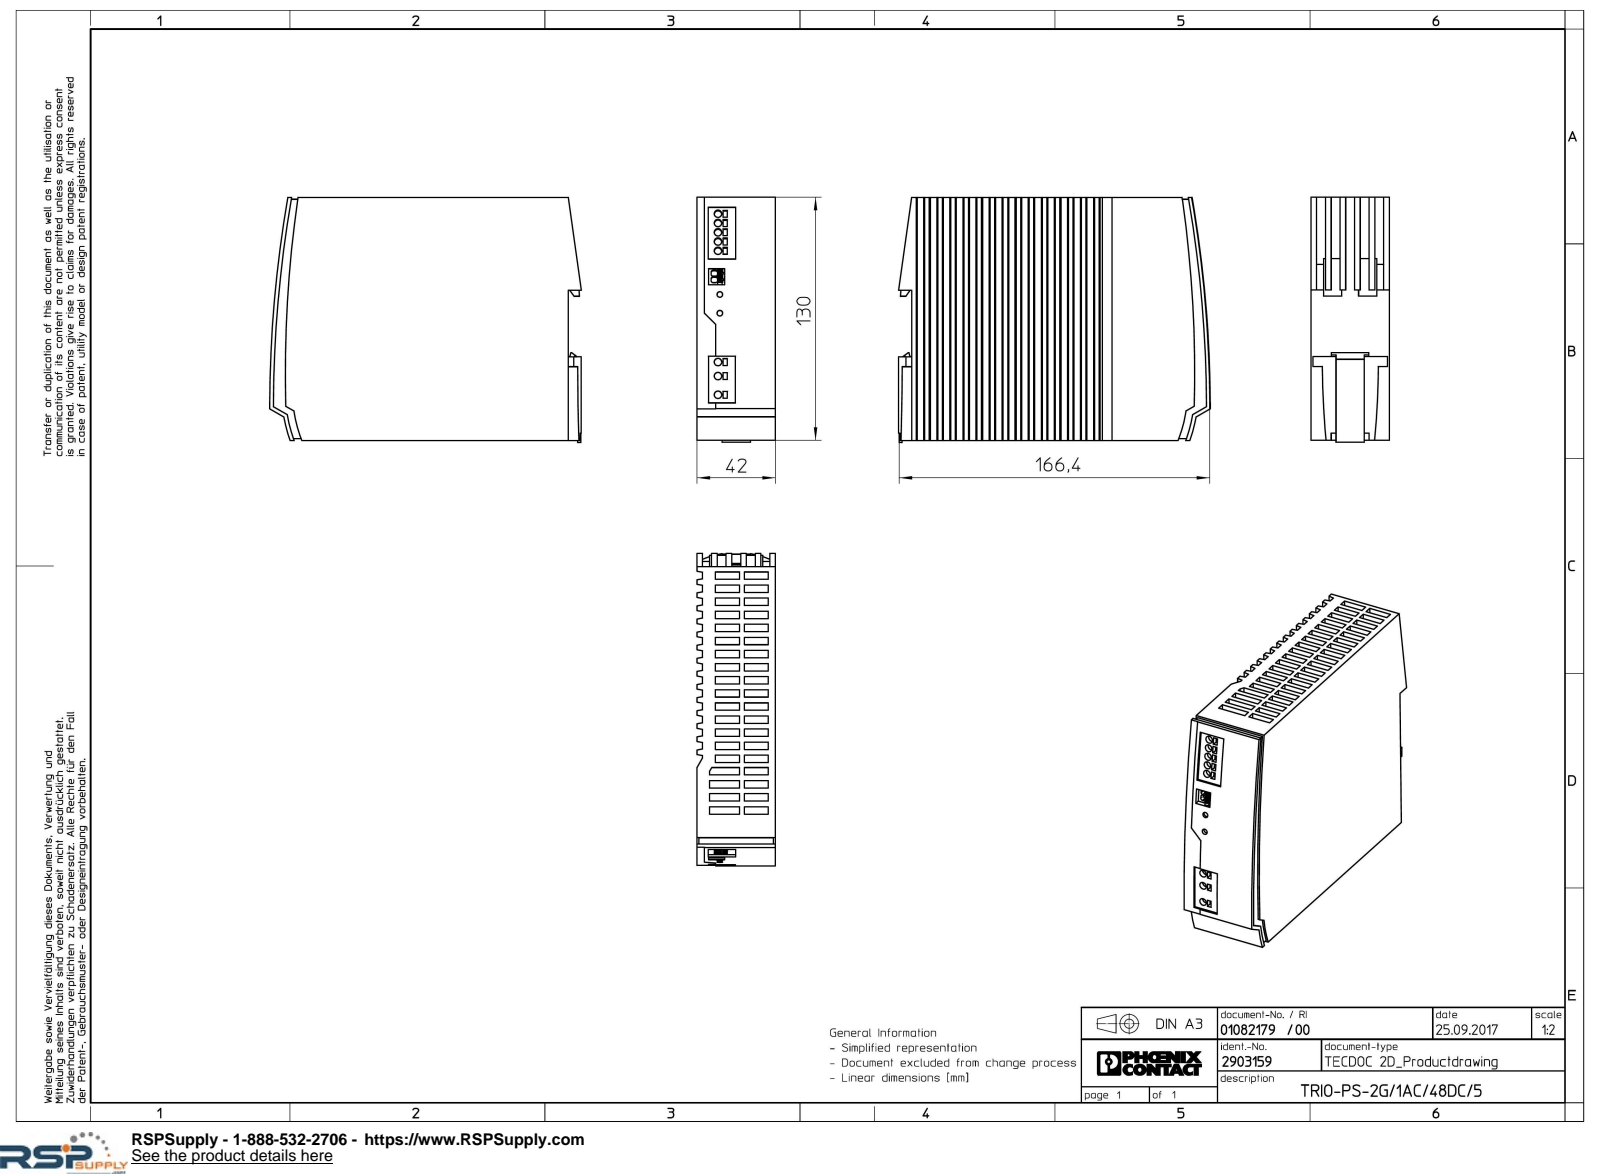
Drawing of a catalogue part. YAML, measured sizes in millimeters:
part_name: "TRIO_PS_2G_1AC_48DC_5-select"
step_written_by: "Creo Elements/Direct Modeling 20.1A 29-Sep-2018 (C) Parametric Technology GmbH (AUTOMOTIVE_DESIGN)"
units: millimeters
bodies: {solids: 1, faces: 694, planar: 647, cylindrical: 43, other: 4}
overall_size: [167, 131, 42]
volume: 826516
surface_area: 86353
round_holes:
  - {diameter: 4, count: 8}
  - {diameter: 3, count: 2}
partial_cylinders:
  - {radius: 0.57, count: 2}
  - {radius: 0.6, count: 2}
  - {radius: 1.03, count: 2}
  - {radius: 1.04, count: 2}
  - {radius: 430, count: 2}
  - {radius: 40, count: 1}
  - {radius: 46.1, count: 1}
  - {radius: 69.15, count: 1}
face_to_face_distances: [3, 42, 13.79, 27.58, 39, 41.37, 6.89, 6.9, 55.16, 20.68]
hole_center_spacings: [5, 10, 7.5, 10.03, 14.99, 15, 17.5, 19.99]
